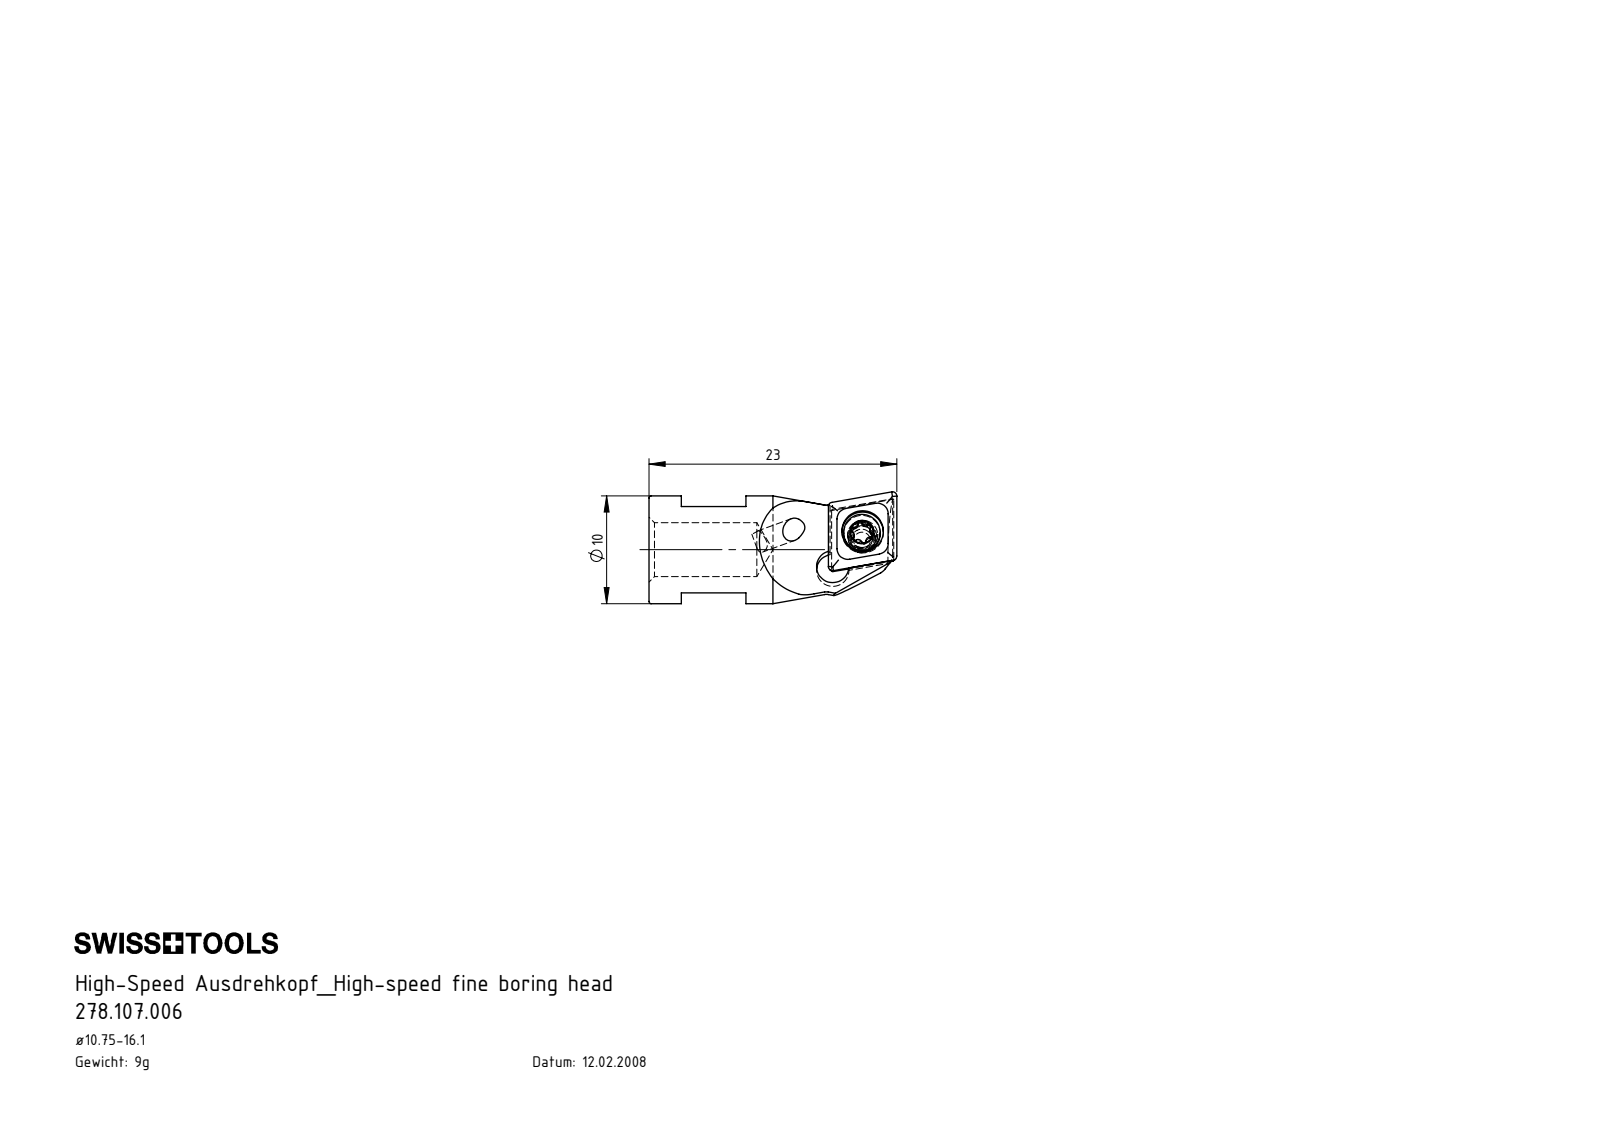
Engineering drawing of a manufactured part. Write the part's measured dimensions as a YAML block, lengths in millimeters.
part_name: "HS6-A11.K11.023_A; WCA-ER2.001.005_A; HS6-A11.K11.023; CCMT060204"
step_written_by: "SolidWorks 2015 (CONFIG_CONTROL_DESIGN)"
units: millimeters
bodies: {solids: 3, faces: 139, planar: 39, cylindrical: 40, other: 60}
overall_size: [23, 10.38, 10.13]
volume: 1061
surface_area: 1149
round_holes:
  - {diameter: 2, count: 1}
  - {diameter: 2.05, count: 1}
  - {diameter: 2.8, count: 1}
  - {diameter: 3.85, count: 1}
  - {diameter: 5, count: 1}
round_bosses_or_shafts:
  - {diameter: 10, count: 1}
  - {diameter: 3.4, count: 1}
  - {diameter: 2.5, count: 1}
partial_cylinders:
  - {radius: 0.21, count: 6}
  - {radius: 0.36, count: 5}
  - {radius: 1, count: 4}
  - {radius: 0.36, count: 1}
  - {radius: 1.4, count: 1}
  - {radius: 1.5, count: 1}
  - {radius: 2, count: 1}
face_to_face_distances: [8.01, 2.29, 2.38, 9, 3, 6, 2.49, 2.58, 16.8, 13.8]
